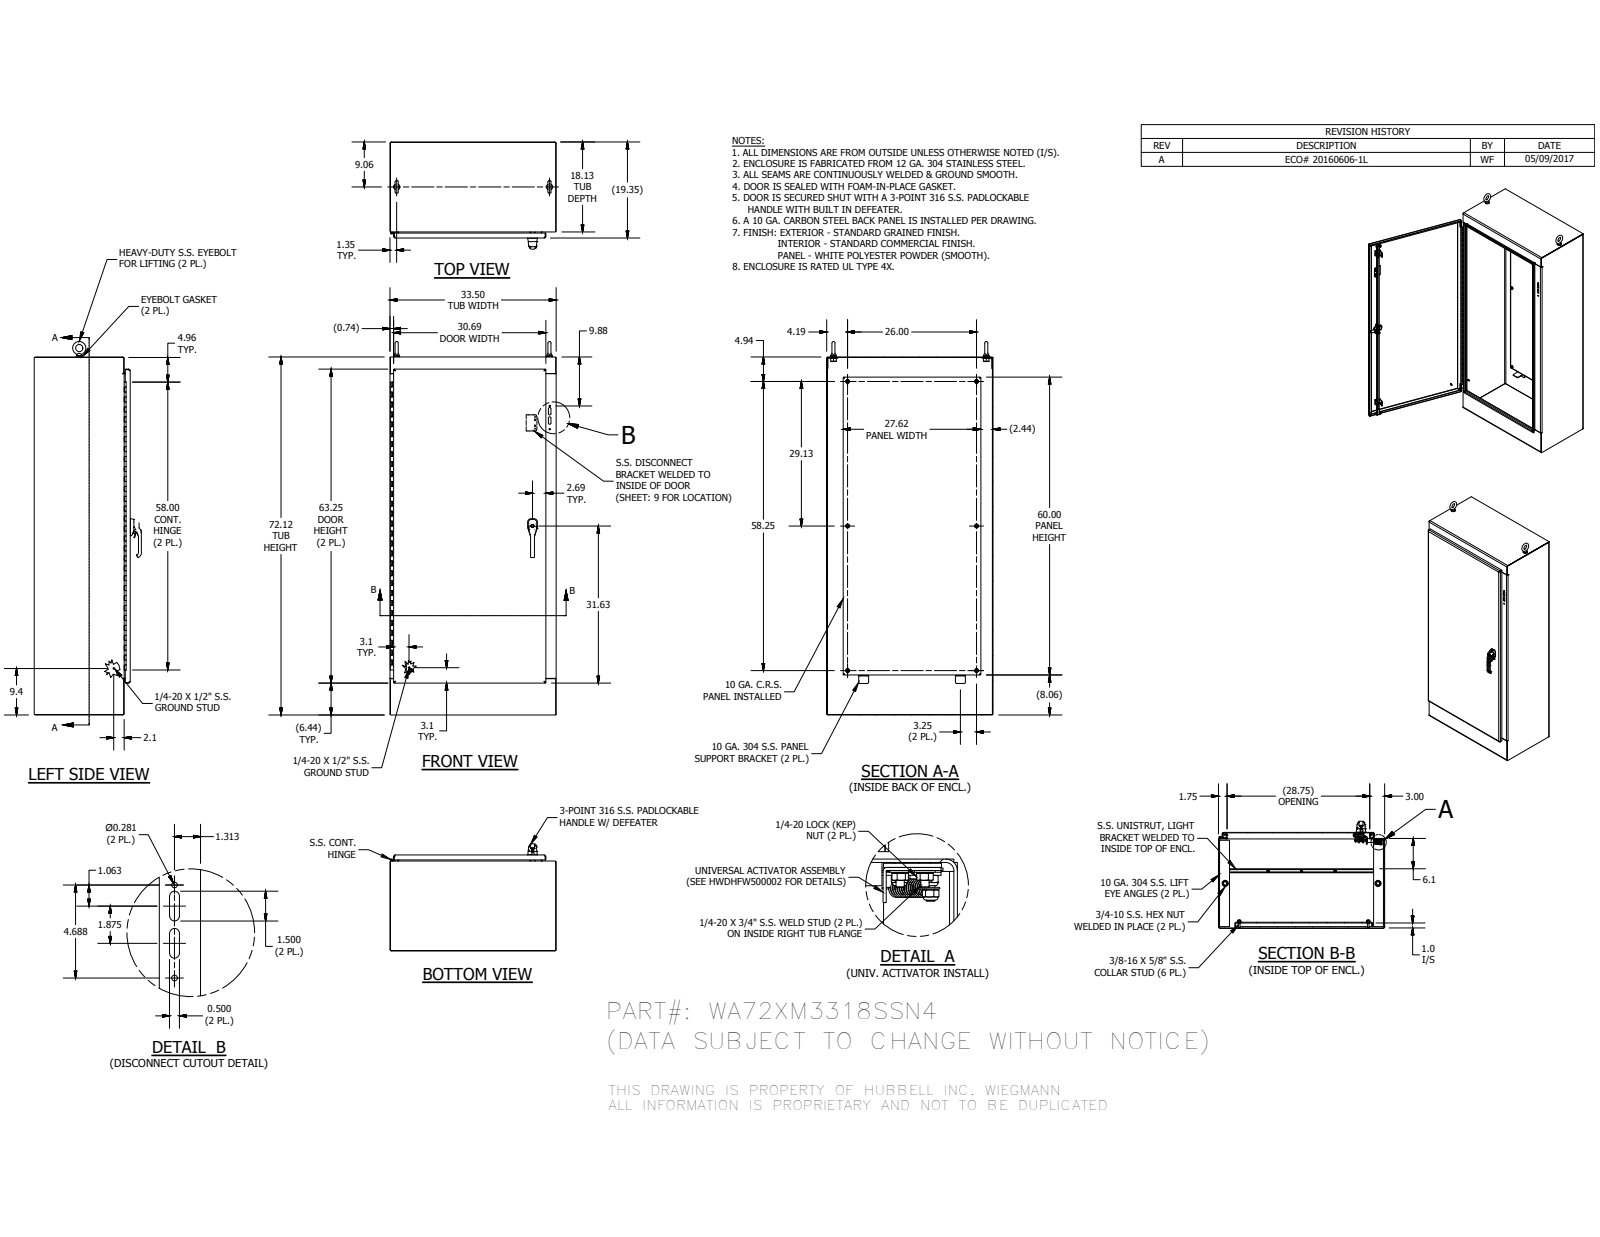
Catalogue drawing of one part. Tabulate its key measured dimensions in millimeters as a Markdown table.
| quantity | value |
| --- | --- |
| part name | WA72XM3318SSN4BLR; WAXM3318SSN4TOP; WAXM3318SSN4BTM; FUN00129_WAXM33SSN4 (+8 more) |
| STEP written by | Autodesk Inventor 2016 (AUTOMOTIVE_DESIGN) |
| units | millimeters |
| bodies | 126 solids, 4763 faces (2197 planar, 1524 cylindrical, 1042 other) |
| overall size | 1911.29 × 850.9 × 548.55 |
| volume | 20 600 000 mm³ |
| surface area | 14 750 000 mm² |
| round holes (diameter × count) | 3.55 × 24, 9.52 × 10, 6.35 × 9, 6.65 × 8, 3.96 × 6, 7.8 × 6, 14.29 × 6, 4.76 × 5, 3.45 × 4, 4.17 × 4, 5.1 × 4, 7.37 × 4 |
| round bosses / shafts (diameter × count) | 15.88 × 10, 8.38 × 9, 14.29 × 6, 13.54 × 4, 8.56 × 4, 6.35 × 4, 6.02 × 4, 6 × 3 |
| partial cylindrical surfaces (radius × count) | 0.5 × 187, 0.3 × 109, 0.51 × 48, 6.35 × 26, 0.47 × 21, 1.59 × 20, 3.17 × 18, 0.64 × 16 |
| main face-to-face distances | 2.64, 488.79, 848.26, 486.15, 491.43, 3.41, 25.4, 845.62, 463.39, 31.45 |
| hole center spacings | 0.45, 163.69, 0.59, 1379.46, 0.74, 9.65, 19.31, 327.38 |
